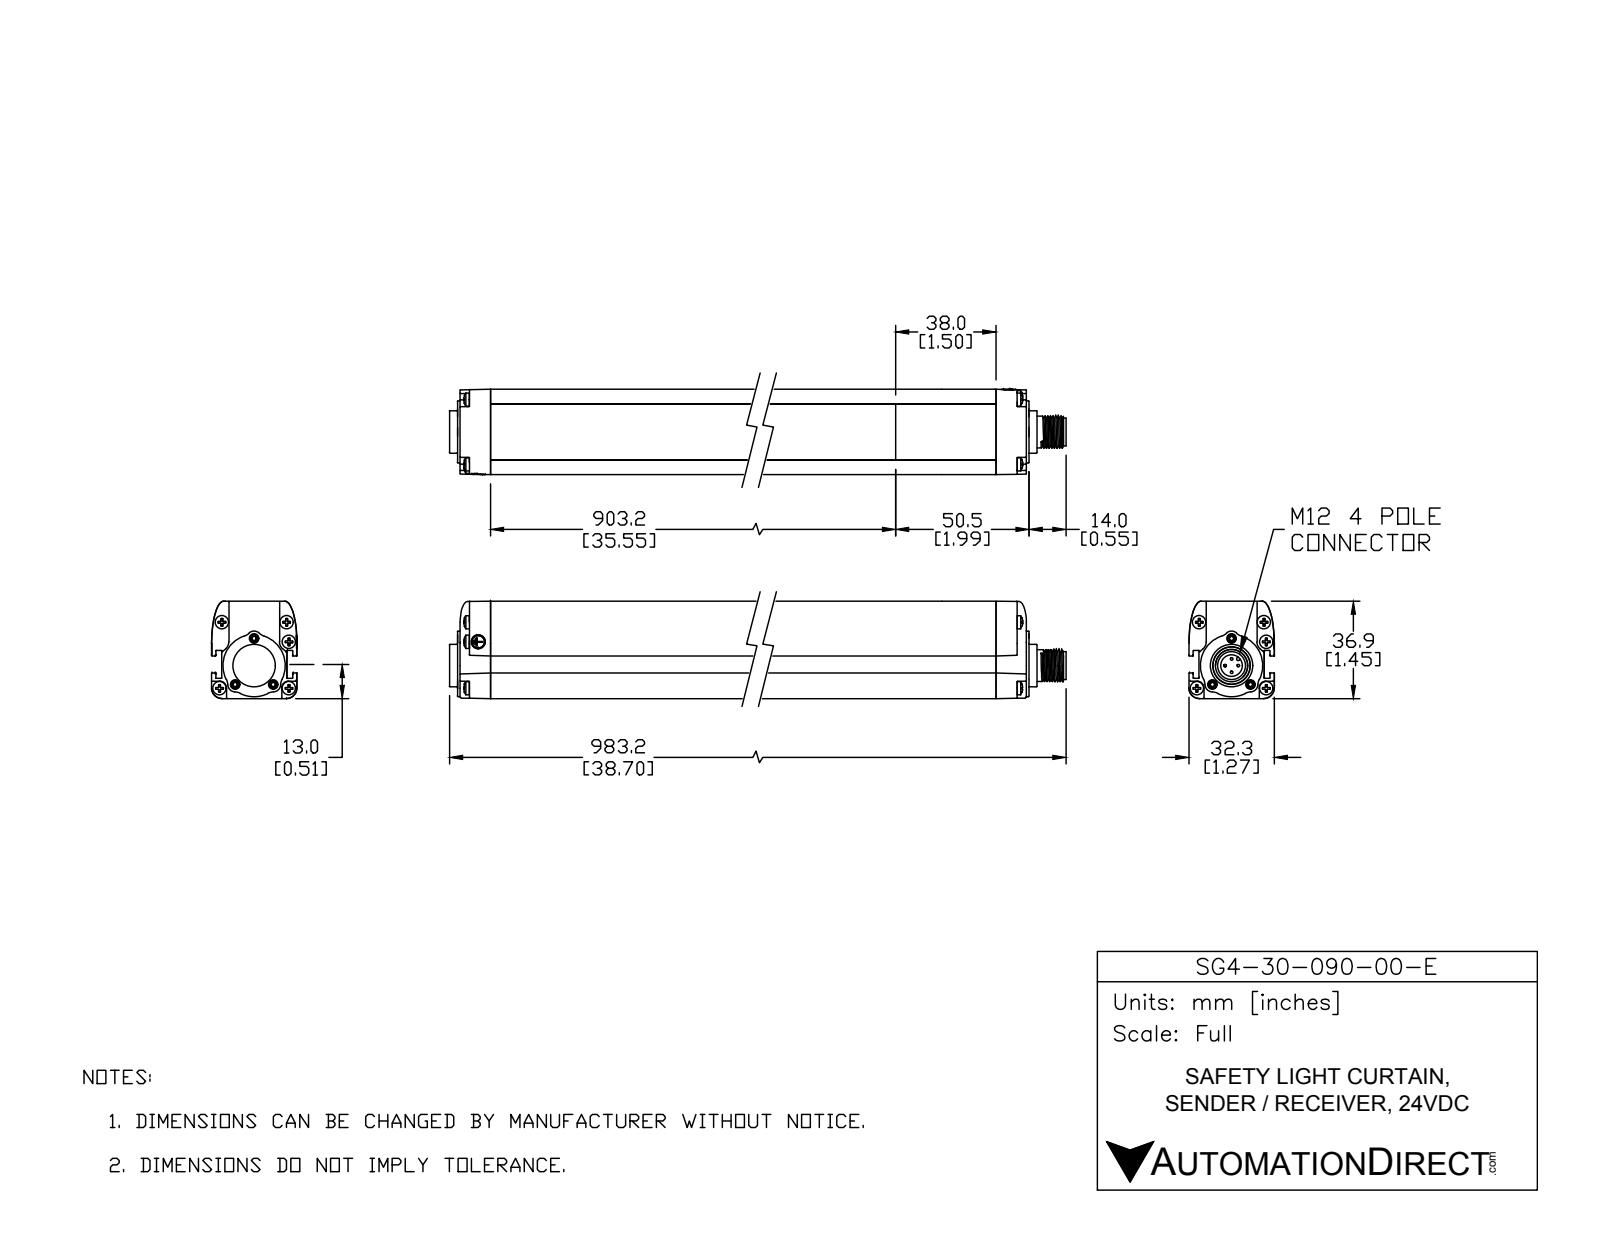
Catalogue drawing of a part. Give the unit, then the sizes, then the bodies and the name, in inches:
Units: inches
Overall size (bounding box): 38.705 × 2.48 × 2.055
Round holes (diameter × count): ⌀0.106 ×6, ⌀0.209 ×6, ⌀0.081 ×4, ⌀0.165 ×4, ⌀0.26 ×4, ⌀0.059 ×3, ⌀0.142 ×3, ⌀0.323 ×1, ⌀0.376 ×1, ⌀0.433 ×1, ⌀0.563 ×1
Round bosses / shafts (diameter × count): ⌀0.197 ×10, ⌀0.394 ×4, ⌀0.039 ×4, ⌀0.185 ×2, ⌀0.63 ×1, ⌀0.55 ×1, ⌀0.472 ×1, ⌀0.413 ×1
Partial cylindrical surfaces — rounded edges, fillets, slot ends (radius × count): R0.008 ×148, R0.004 ×120, R0.006 ×18, R0.106 ×18, R0.118 ×8, R0.197 ×7, R0.11 ×3, R0.016 ×2
Main face-to-face distances: 0.079, 1.272, 1.429, 0.15, 1.122, 1.35, 0.157, 0.972, 0.333, 0.063
Hole centre spacings: 0.569, 35.477, 0.402, 0.24, 0.293, 0.52, 0.541, 0.619
Volume: 61.68 in³ · Surface area: 378.8 in²
Bodies: 29 solids, 1674 faces (410 planar, 591 cylindrical, 673 other)
Part name (STEP PRODUCT): SG4-30-090-OO-E
STEP written by: SolidWorks 2017 (AUTOMOTIVE_DESIGN)
